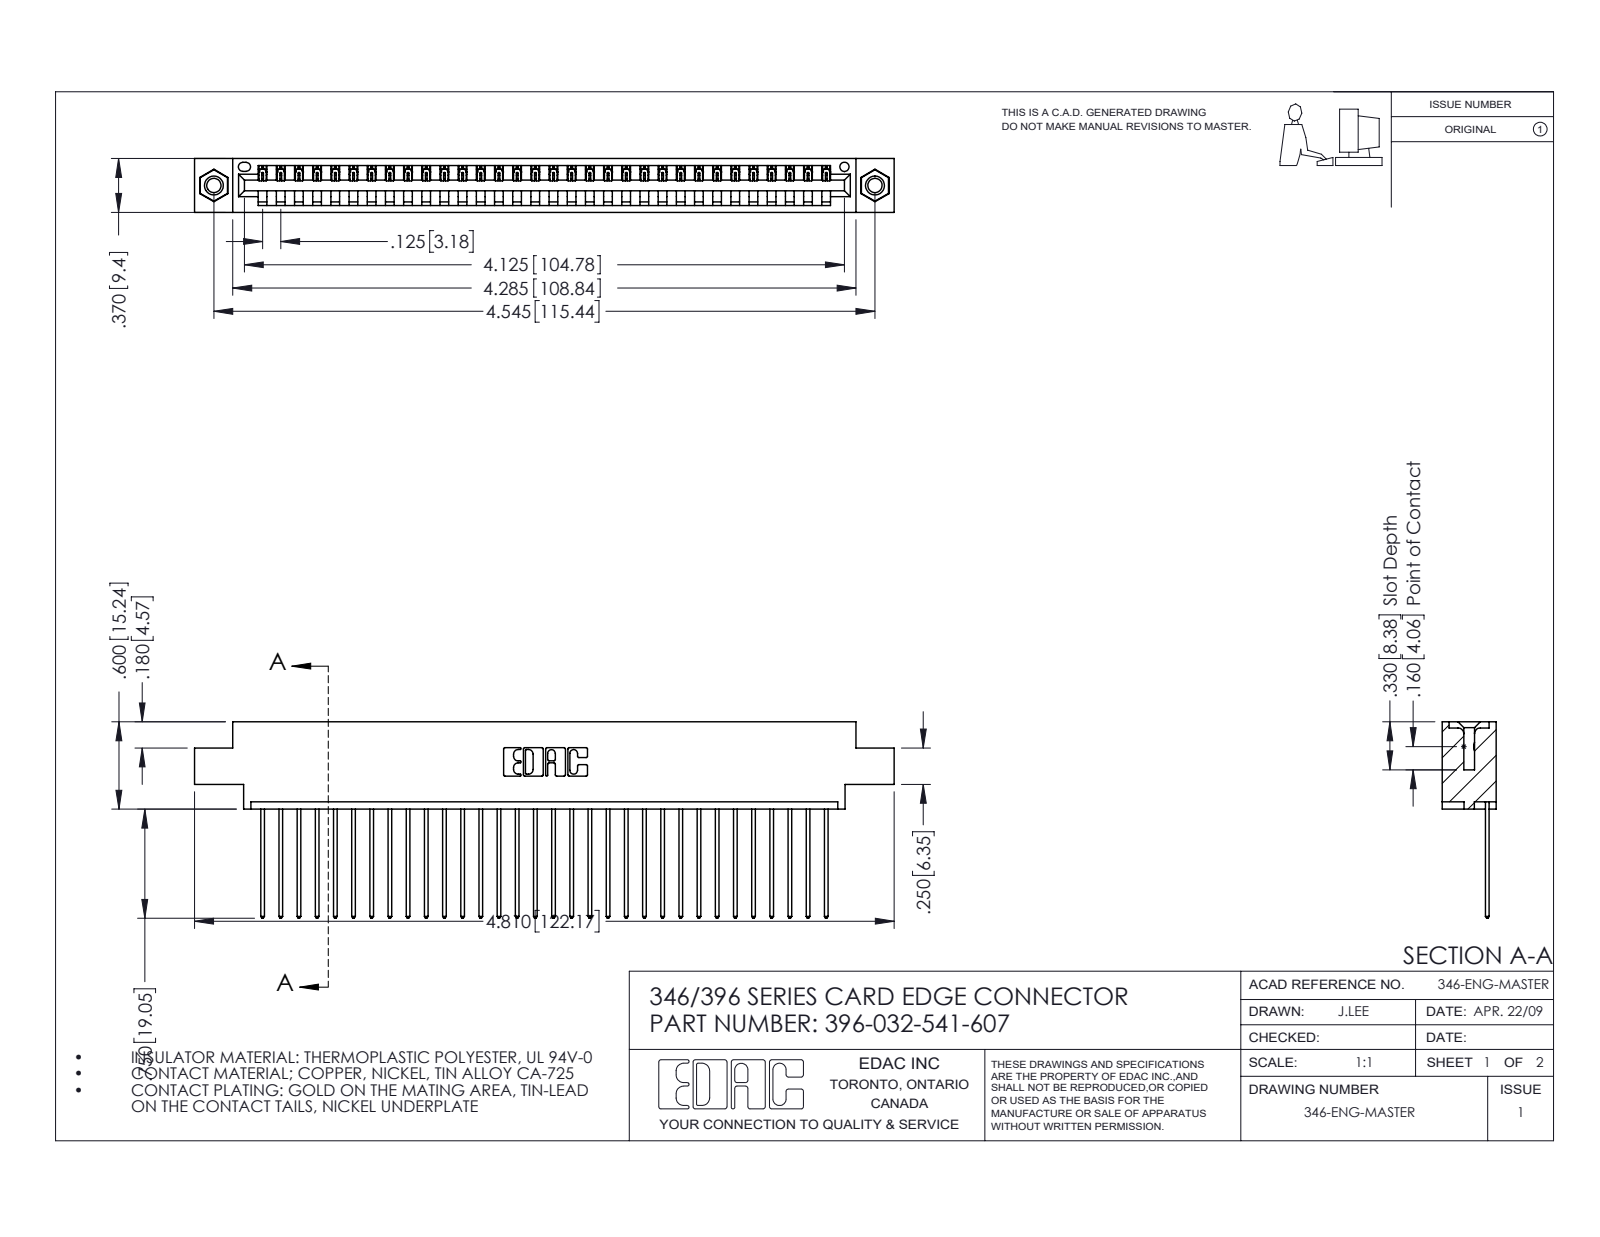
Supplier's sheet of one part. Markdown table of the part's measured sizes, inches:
| quantity | value |
| --- | --- |
| part name | 345-250-001_345-250-005-103; 346 Part_0.170 Offset - 0.156 Dia-TI; 345-292-001_345-293-141; 396-032-541-607 |
| STEP written by | SolidWorks 2016 (CONFIG_CONTROL_DESIGN) |
| units | inches |
| bodies | 35 solids, 2042 faces (1392 planar, 634 cylindrical, 16 other) |
| overall size | 4.81 × 1.35 × 0.37 |
| volume | 0.706 in³ |
| surface area | 23.51 in² |
| round holes (diameter × count) | 0.098 × 2, 0.125 × 2, 0.156 × 2, 0.064 × 1 |
| round bosses / shafts (diameter × count) | 0.155 × 2 |
| partial cylindrical surfaces (radius × count) | 0.006 × 64, 0.01 × 64, 0.01 × 22, 0.007 × 6, 0.031 × 6, 0.026 × 3, 0.031 × 2, 0.04 × 2 |
| main face-to-face distances | 0.048, 0.322, 0.37, 0.25, 0.072, 0.298, 0.025, 0.222, 0.148, 0.1 |
| hole center spacings | 0.246, 4.337, 4.545 |
